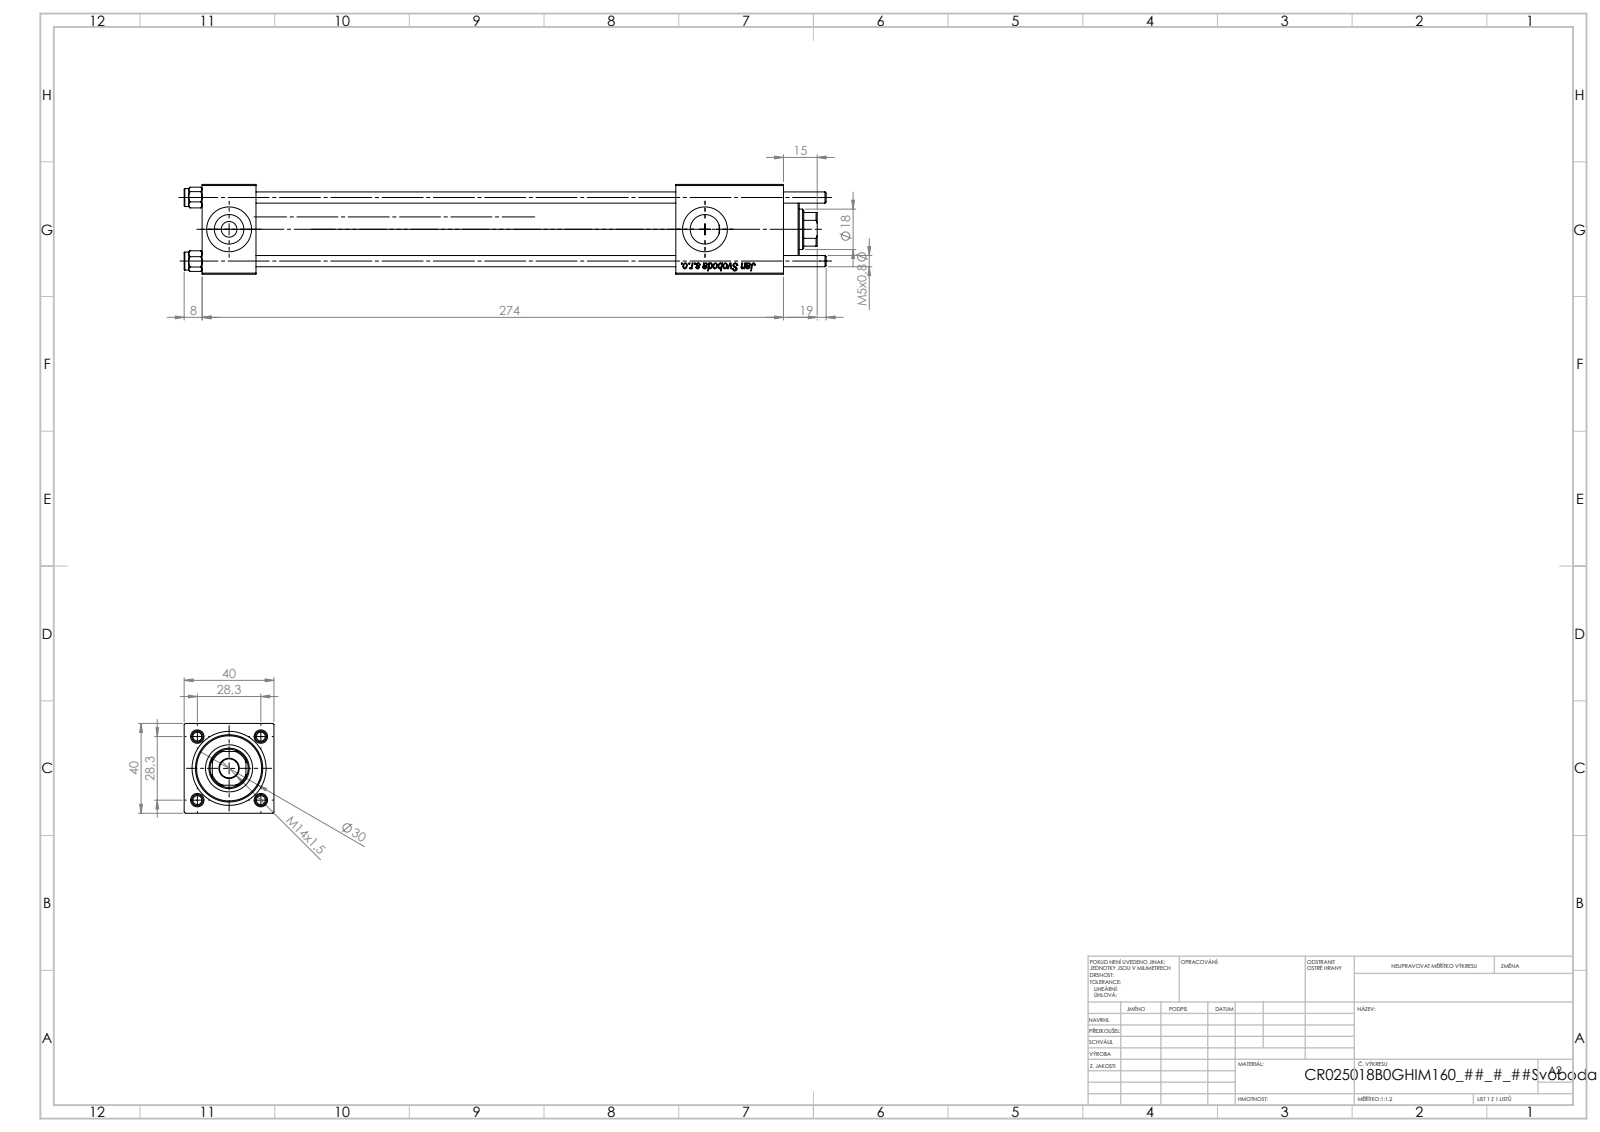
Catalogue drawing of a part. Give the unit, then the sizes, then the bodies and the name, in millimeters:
Units: millimetres
Overall size (bounding box): 286 × 40 × 40
Round holes (diameter × count): ⌀5 ×4, ⌀20 ×3, ⌀7 ×2, ⌀13.16 ×2, ⌀8.5 ×1, ⌀18 ×1, ⌀21 ×1, ⌀25 ×1, ⌀30 ×1
Round bosses / shafts (diameter × count): ⌀8 ×4, ⌀31 ×1
Partial cylindrical surfaces — rounded edges, fillets, slot ends (radius × count): R8.5 ×1
Main face-to-face distances: 40, 24, 211, 187, 230.3, 206.3, 19.3, 259, 235, 48
Hole centre spacings: 20.01, 28.3, 40.02, 212
Volume: 236 057 mm³ · Surface area: 102 238 mm²
Bodies: 11 solids, 1152 faces (428 planar, 76 cylindrical, 648 other)
Part name (STEP PRODUCT): V215_VC_A; V215CR_VCP_B; V215CR_B-1; V215CR_B_TYCINKA (+1 more)
STEP written by: SolidWorks 2019 (CONFIG_CONTROL_DESIGN)
